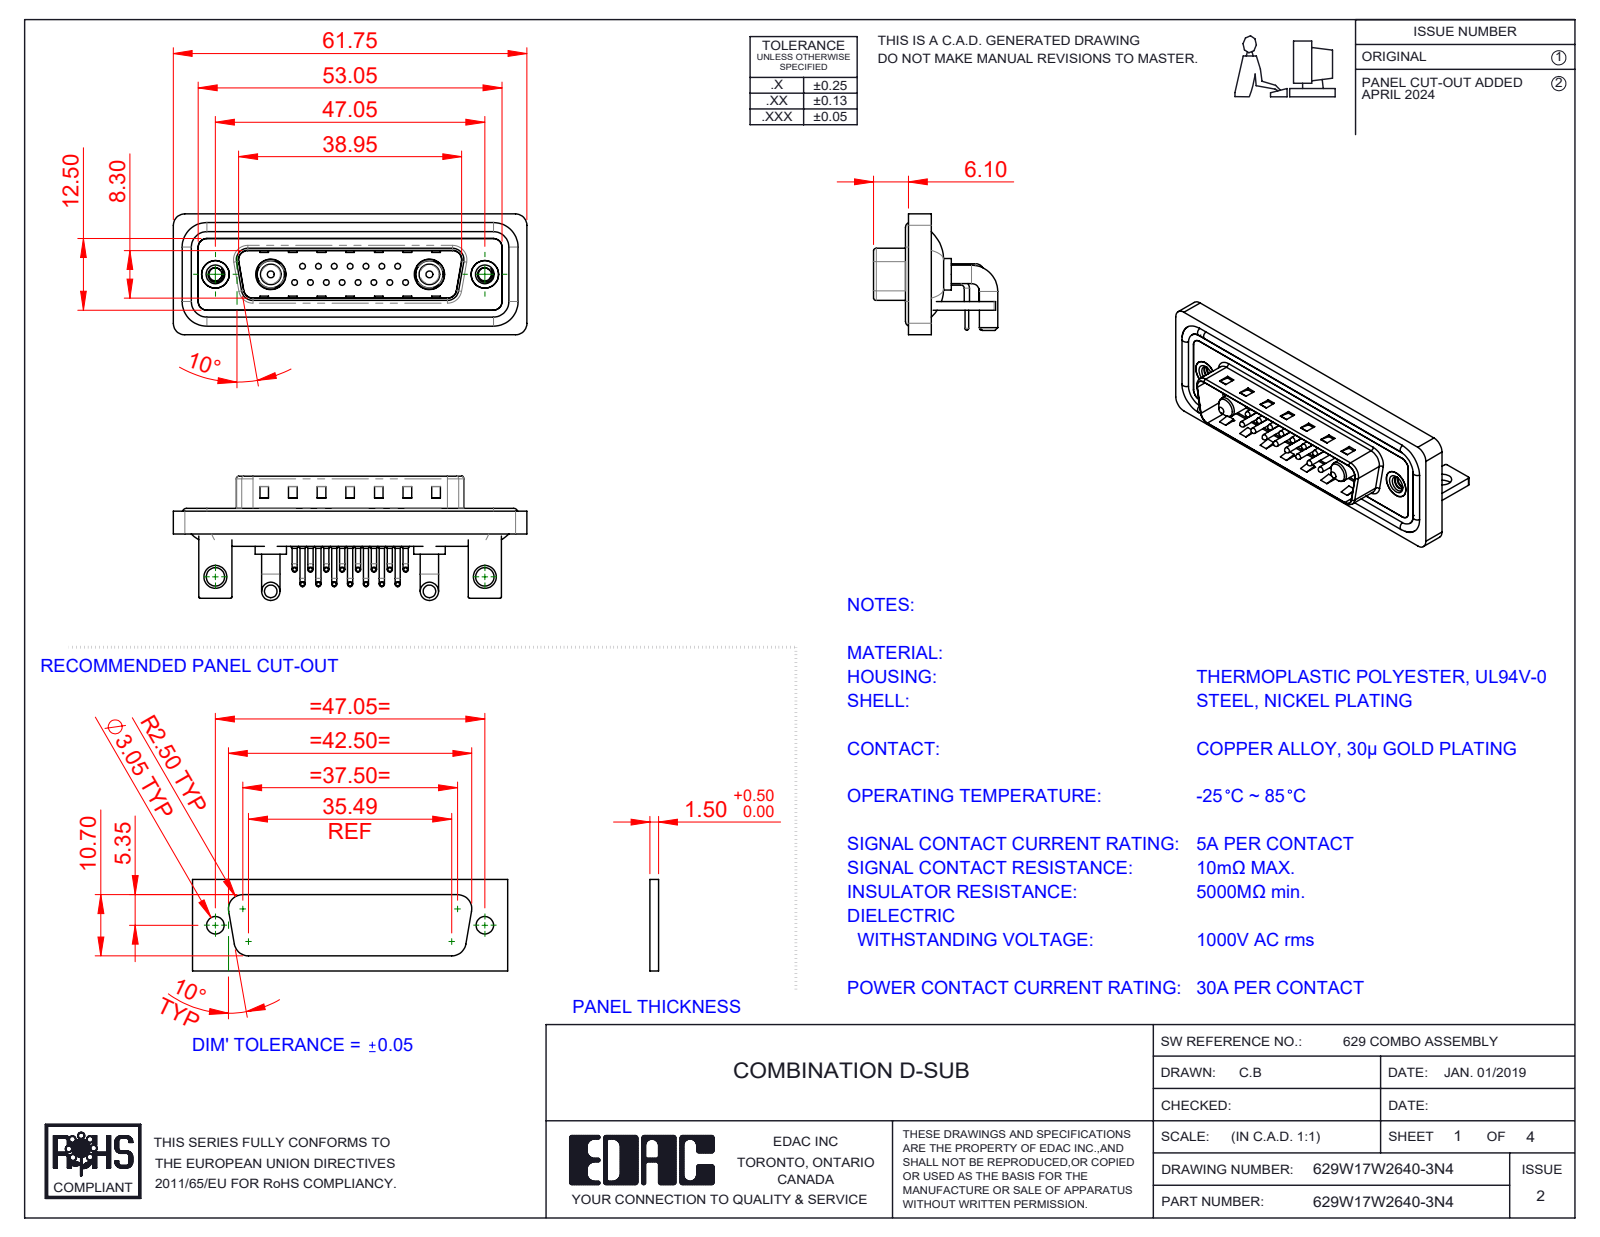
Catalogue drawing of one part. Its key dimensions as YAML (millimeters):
part_name: "629Combo Housing_17W2; 629Combo Shell Rear_25 Contacts; 629W17W2640-3N4; 629Combo Waterproof Housing_25 Contacts (+6 more)"
step_written_by: "SolidWorks 2023 (CONFIG_CONTROL_DESIGN)"
units: millimeters
bodies: {solids: 28, faces: 2259, planar: 1209, cylindrical: 788, other: 262}
overall_size: [61.75, 21.7, 21.1]
volume: 7846
surface_area: 13225
round_holes:
  - {diameter: 0.75, count: 15}
  - {diameter: 1.6, count: 15}
  - {diameter: 2, count: 15}
  - {diameter: 2.26, count: 2}
  - {diameter: 3.2, count: 2}
  - {diameter: 4, count: 2}
  - {diameter: 4.8, count: 2}
  - {diameter: 4.85, count: 2}
  - {diameter: 5, count: 2}
  - {diameter: 5.3, count: 2}
round_bosses_or_shafts:
  - {diameter: 0.9, count: 30}
  - {diameter: 1.5, count: 15}
  - {diameter: 1, count: 15}
  - {diameter: 0.65, count: 15}
  - {diameter: 3.2, count: 4}
  - {diameter: 1.6, count: 4}
  - {diameter: 5.5, count: 2}
  - {diameter: 5.2, count: 2}
partial_cylinders:
  - {radius: 2, count: 19}
  - {radius: 1.5, count: 18}
  - {radius: 0.25, count: 16}
  - {radius: 1.01, count: 15}
  - {radius: 0.5, count: 9}
  - {radius: 1.6, count: 8}
  - {radius: 0.6, count: 4}
  - {radius: 0.65, count: 4}
face_to_face_distances: [0.4, 0.8, 1.5, 2.1, 2.9, 1.1, 4.1, 1.6, 4.5, 3.7]
hole_center_spacings: [3.16, 2.77, 5.54, 8.31, 5.04, 7.49, 11.08, 5.03]
